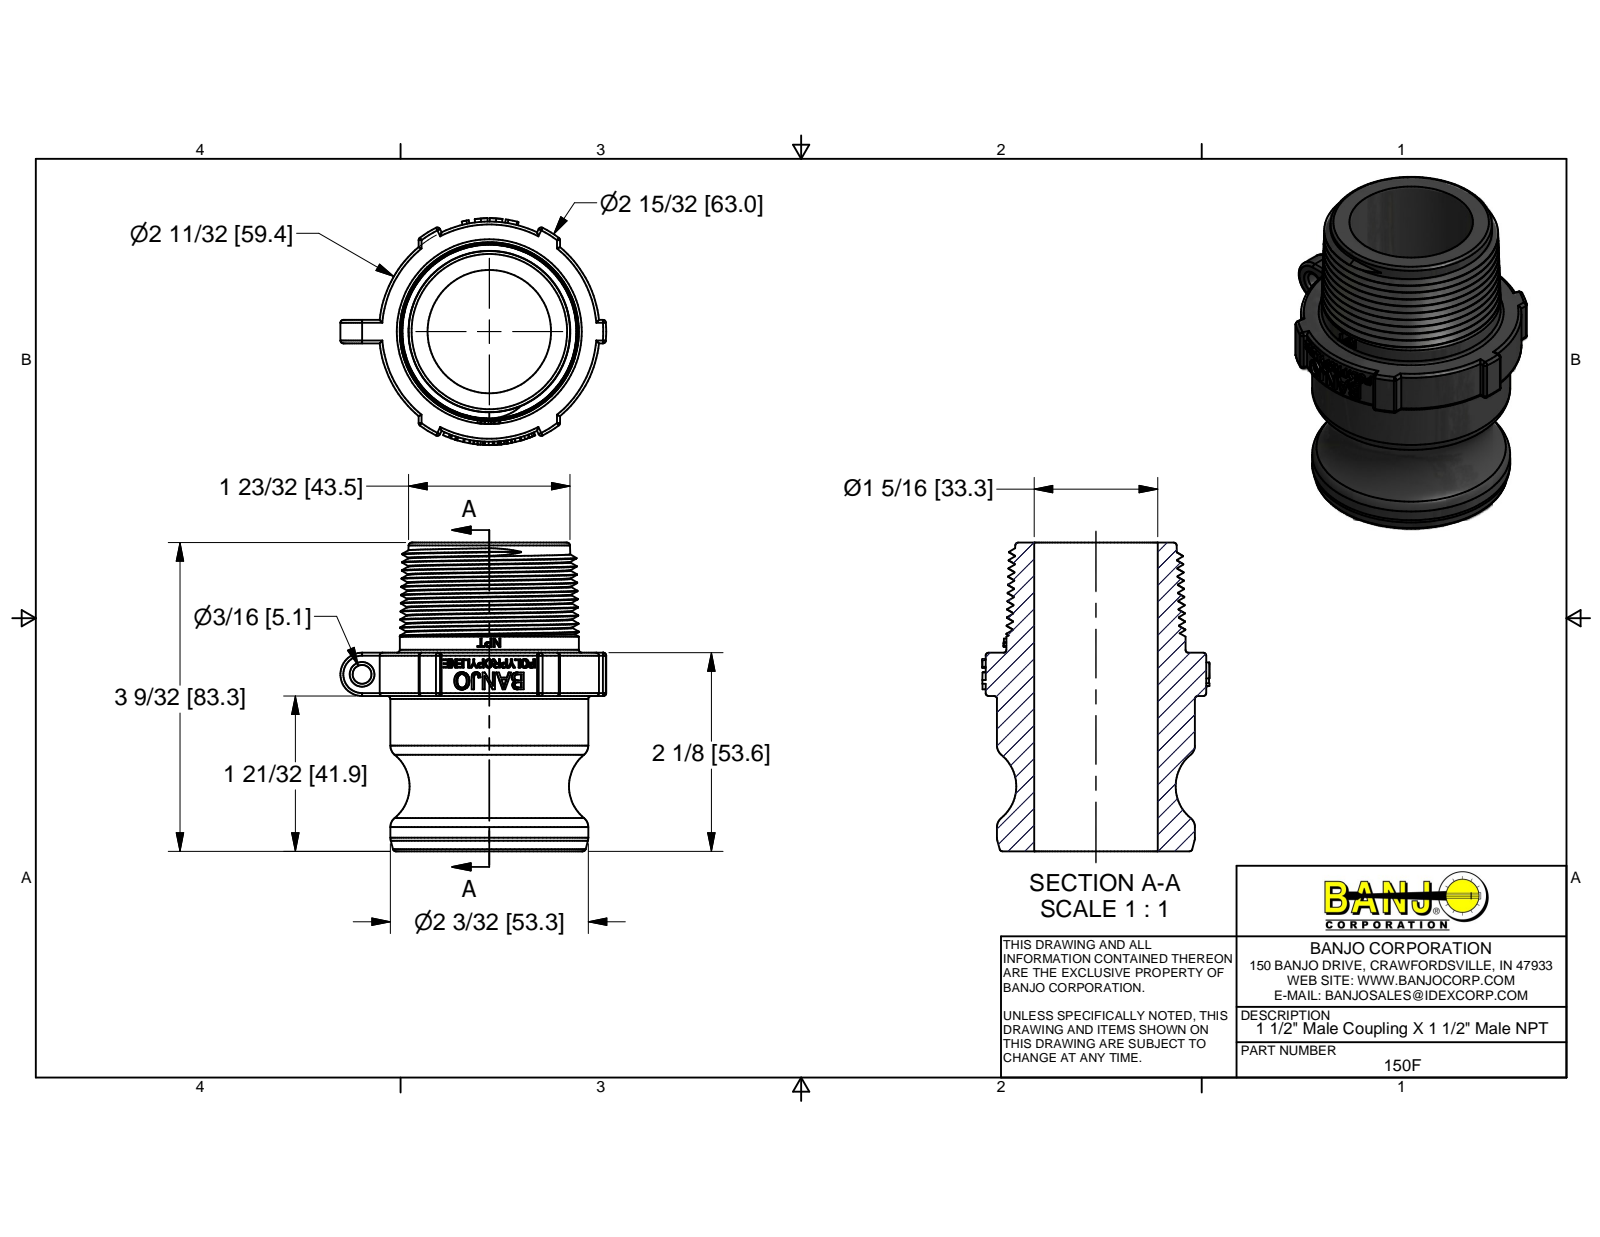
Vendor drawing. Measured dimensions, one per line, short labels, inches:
name: 150F
written by: Autodesk Inventor 2014 (AUTOMOTIVE_DESIGN)
unit: in
bodies: 1 solid, 443 faces (178 planar, 89 cylindrical, 176 other)
size: 3.28 × 2.82 × 2.41
volume: 5.707 in³; area: 45.06 in²
holes: 1× ⌀0.2, 1× ⌀1.31
bosses: 1× ⌀2.1, 1× ⌀1.9
rounds: 26× R0.031, 1× R0.23, 1× R0.494, 1× R0.98, 1× R1.17, 1× R1.205, 1× R1.24
face distances: 2.11, 3.28, 1.17, 1.65, 0.46, 1.63, 0.25, 1.5, 0.25, 0.09
